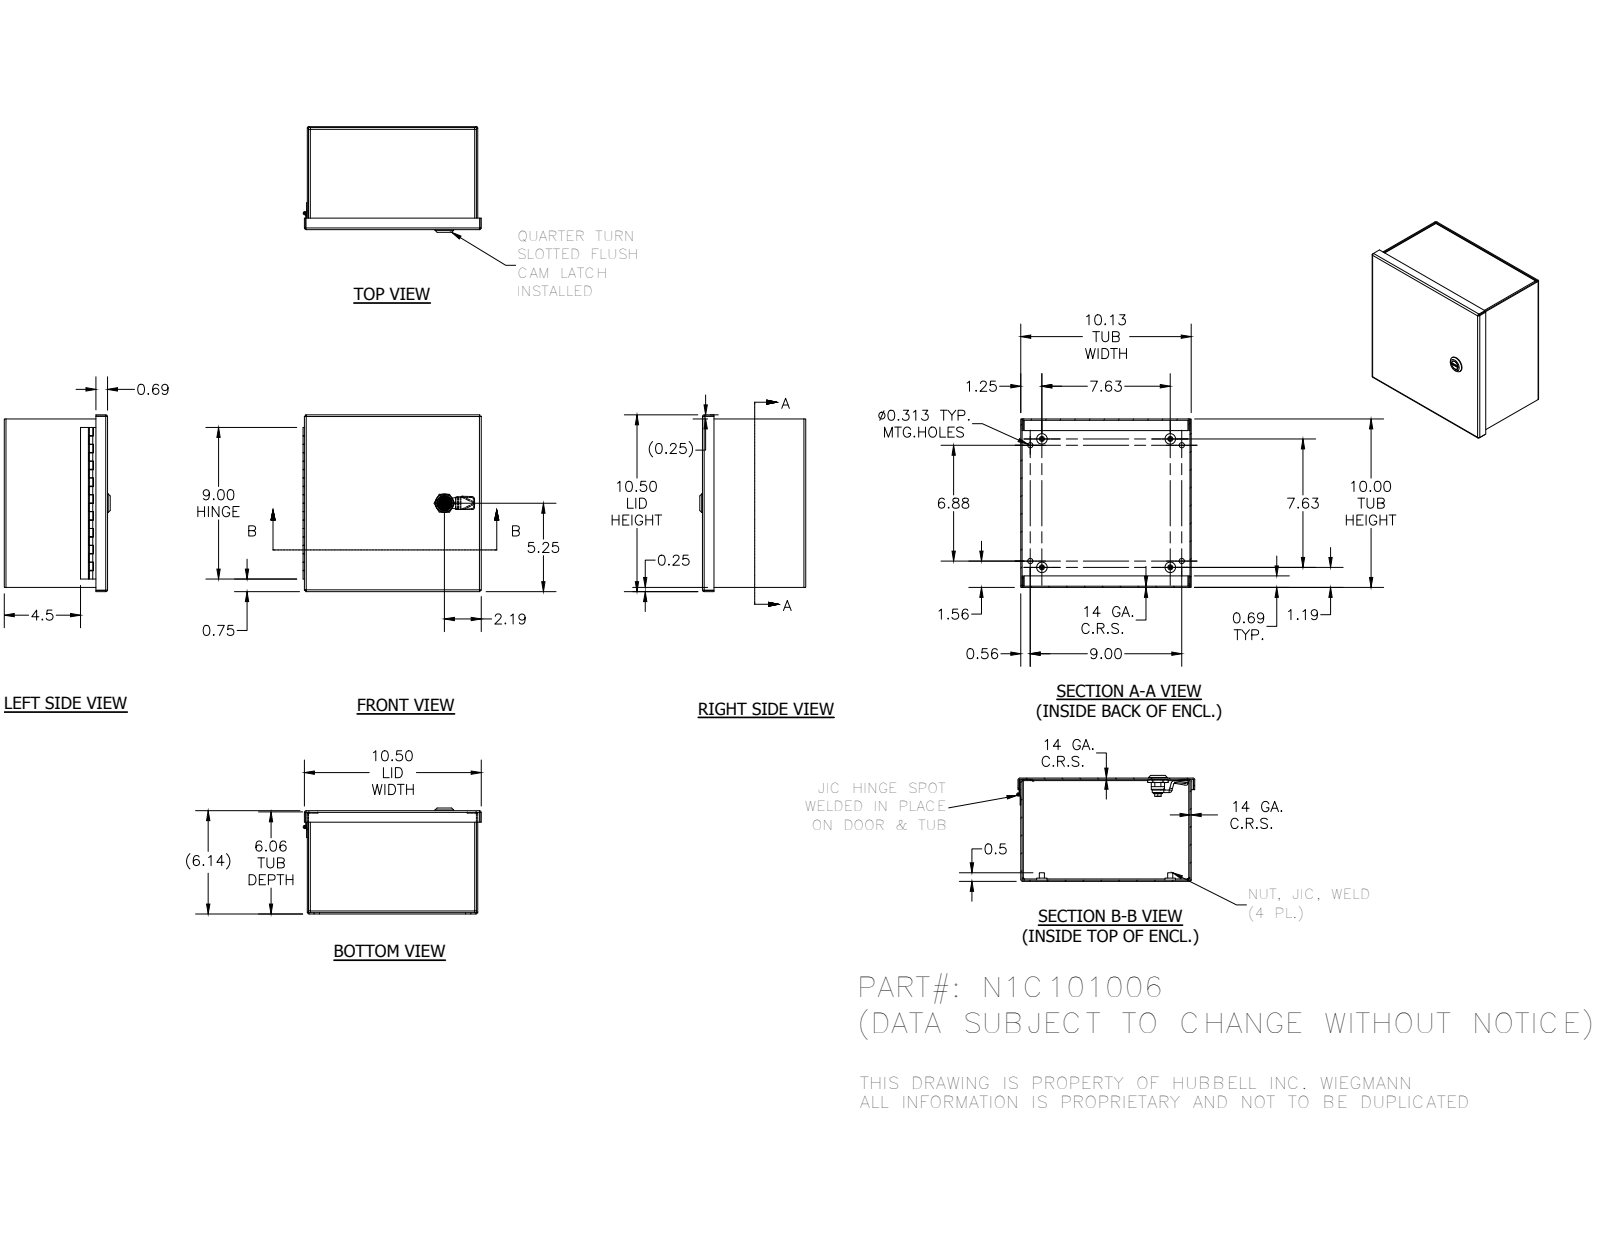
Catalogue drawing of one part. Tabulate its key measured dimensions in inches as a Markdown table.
| quantity | value |
| --- | --- |
| part name | N1C_SMALL; N1C1006TB; N1C101006BLR; HFW3513 (+8 more) |
| STEP written by | Autodesk Inventor 2012 (AUTOMOTIVE_DESIGN) |
| units | inches |
| bodies | 19 solids, 695 faces (399 planar, 214 cylindrical, 82 other) |
| overall size | 10.584 × 10.5 × 6.294 |
| volume | 40.16 in³ |
| surface area | 1 111 in² |
| round holes (diameter × count) | 0.156 × 4, 0.313 × 4, 0.116 × 1, 0.197 × 1, 0.315 × 1, 0.394 × 1, 0.402 × 1, 0.634 × 1, 0.802 × 1 |
| round bosses / shafts (diameter × count) | 0.625 × 4, 0.3 × 4, 1.102 × 1, 0.866 × 1, 0.78 × 1, 0.63 × 1, 0.598 × 1, 0.531 × 1 |
| partial cylindrical surfaces (radius × count) | 0.012 × 30, 0.031 × 16, 0.105 × 16, 0.02 × 10, 0.157 × 4, 0.016 × 3, 0.039 × 1, 0.173 × 1 |
| main face-to-face distances | 0.074, 6.063, 5.989, 10.051, 9.926, 6.137, 9.977, 10.125, 10, 9.852 |
| hole center spacings | 0.783, 7.283, 7.625, 8.321, 11.03, 3.718, 3.882, 6.875 |
